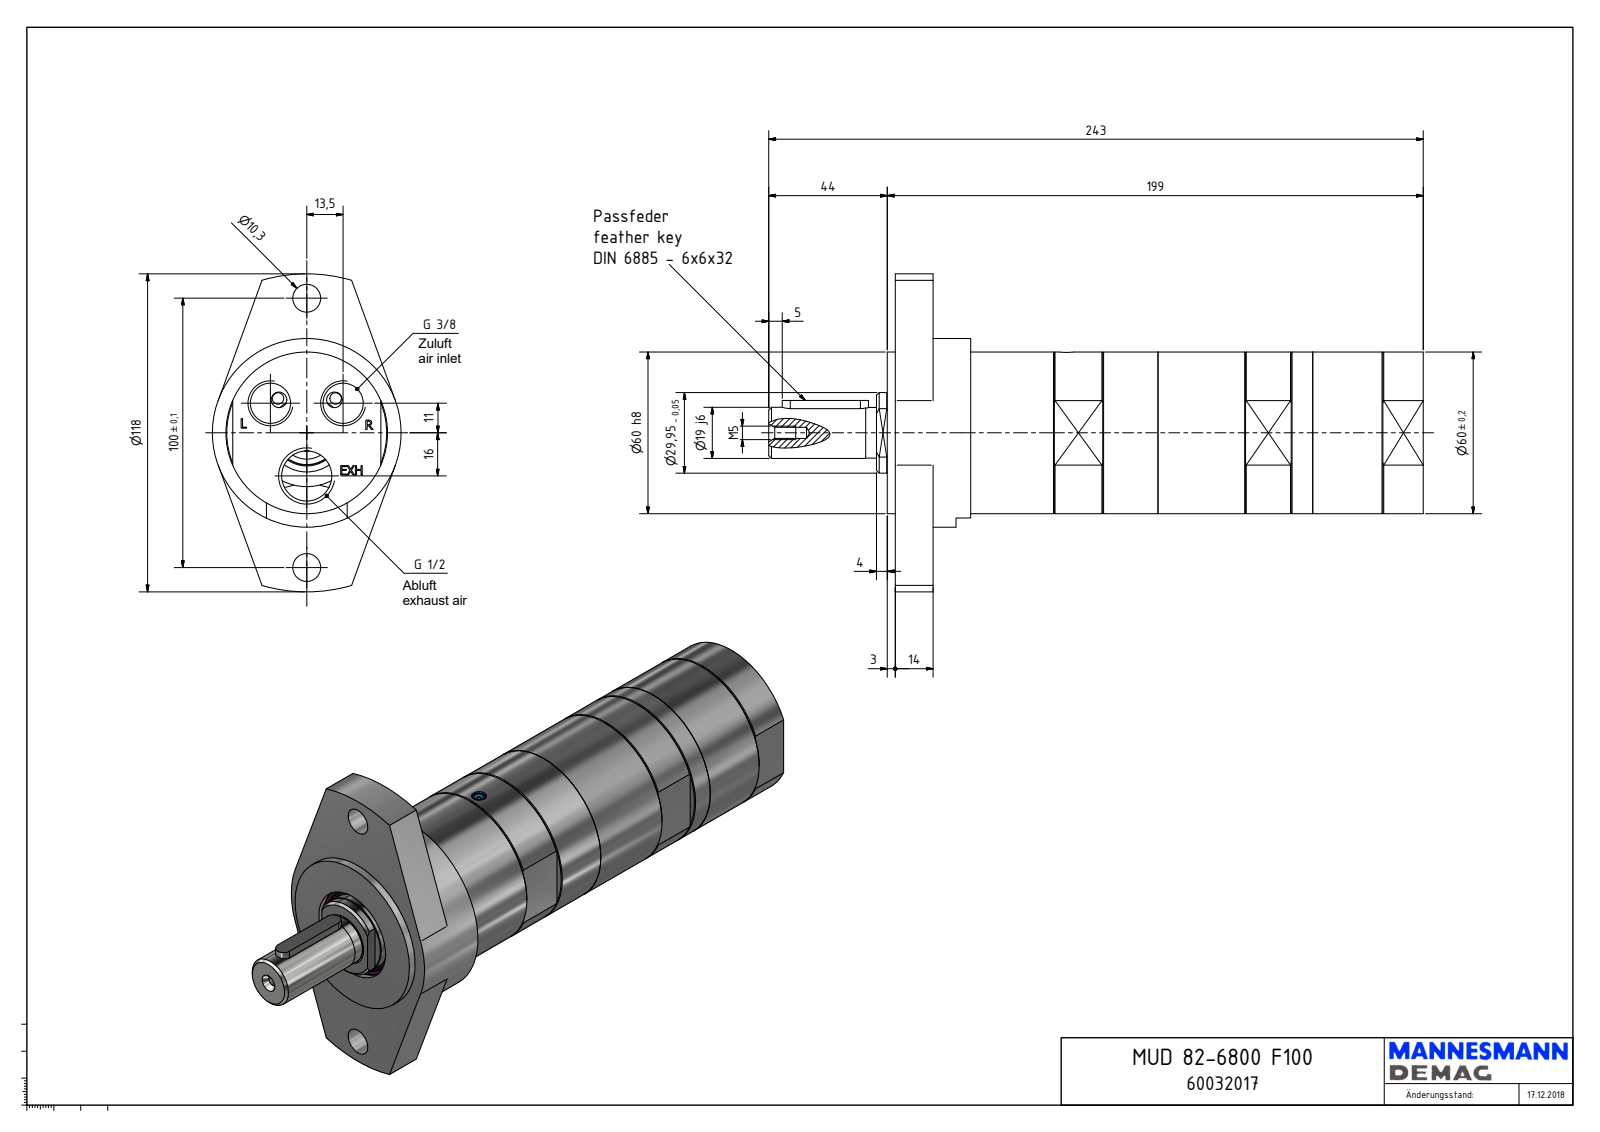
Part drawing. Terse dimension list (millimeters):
name: MUD 82-6800 F100_60032017
written by: Autodesk Inventor 2018 (AUTOMOTIVE_DESIGN)
unit: mm
bodies: 1 solid, 201 faces (115 planar, 47 cylindrical, 39 other)
size: 243 × 118 × 70
volume: 615 998 mm³; area: 62 124 mm²
holes: 2× ⌀10.3, 2× ⌀14.95, 1× ⌀1.55, 1× ⌀4, 1× ⌀4.13, 1× ⌀5.5, 1× ⌀18.63, 1× ⌀35
bosses: 1× ⌀70, 1× ⌀60, 1× ⌀55.18, 1× ⌀29.95, 1× ⌀19, 1× ⌀18.8, 1× ⌀5, 1× ⌀3.6
rounds: 2× R3, 2× R7.5, 1× R8.5, 1× R19.02, 1× R23.5, 1× R25.67, 1× R59
face distances: 14, 17, 3, 196, 182, 199, 55, 31, 28, 168
hole spacings: 17.41, 30.19, 41.27, 50, 62.48, 16, 27, 34
